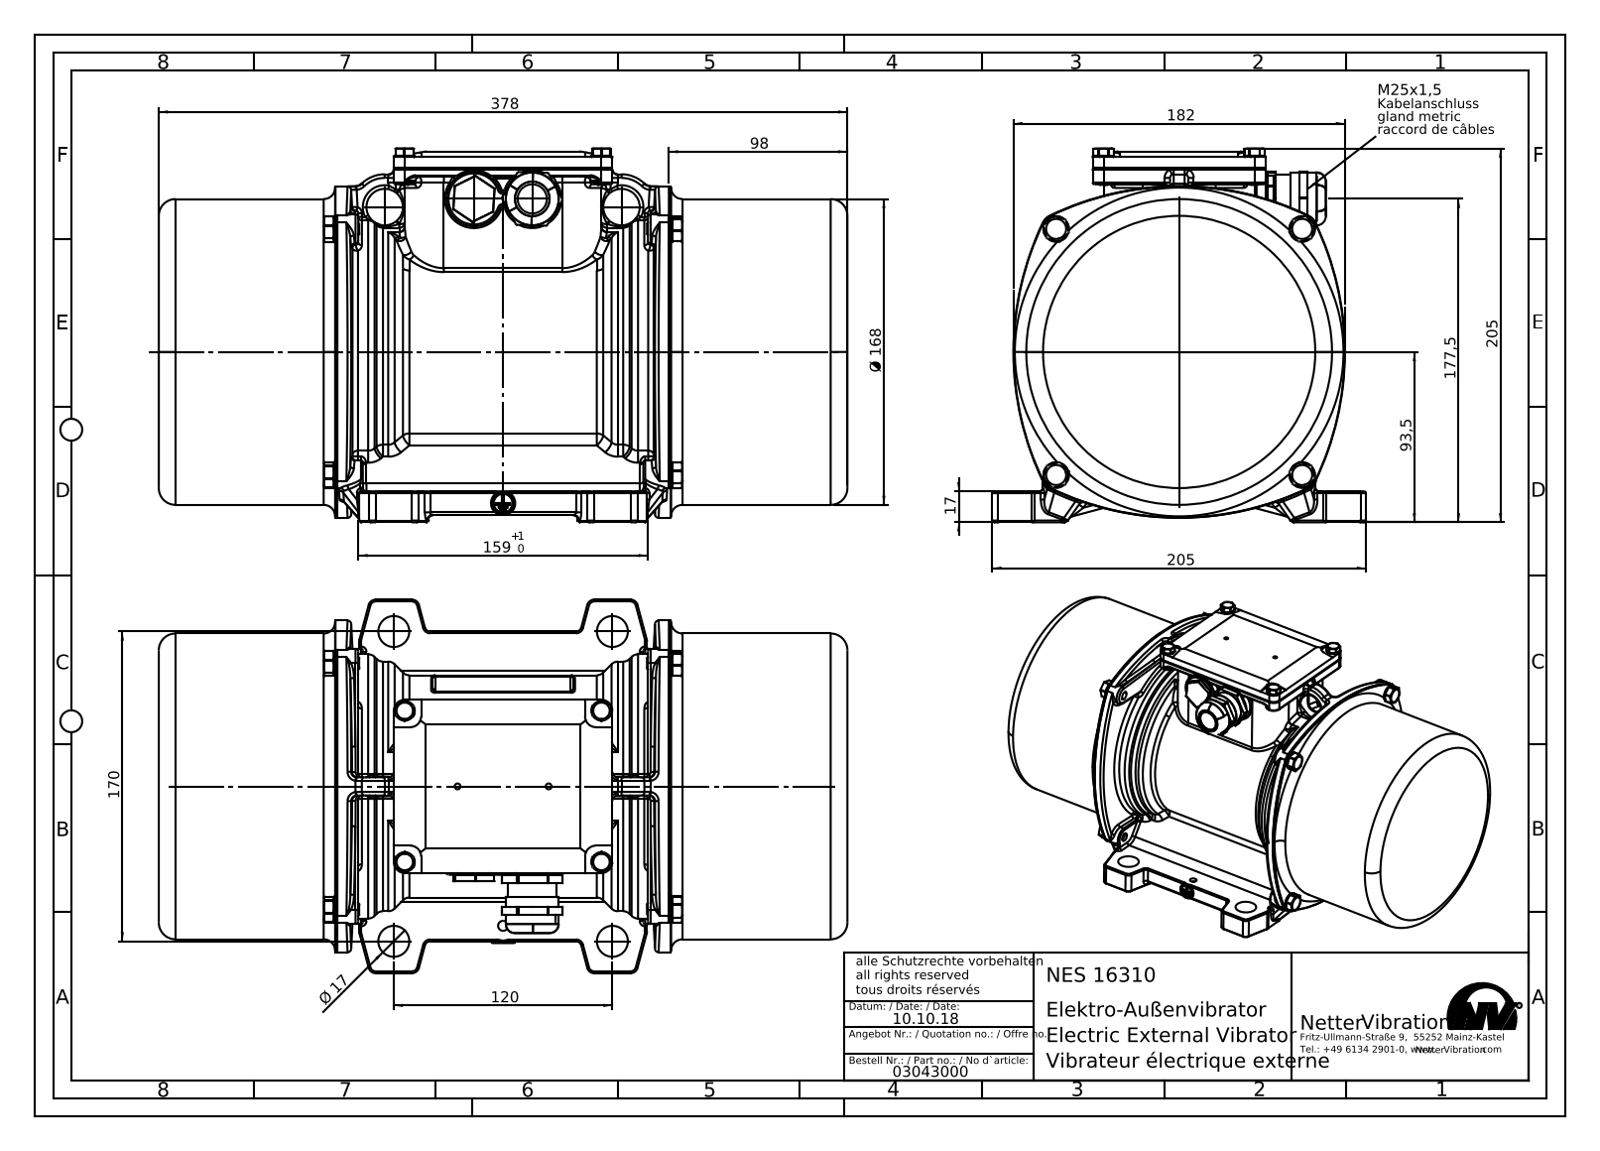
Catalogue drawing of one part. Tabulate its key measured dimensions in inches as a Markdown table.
| quantity | value |
| --- | --- |
| part name | NES 16320 #03043000 |
| STEP written by | SolidWorks 2010 (AUTOMOTIVE_DESIGN) |
| units | inches |
| bodies | 8 solids, 4055 faces (1849 planar, 731 cylindrical, 1475 other) |
| overall size | 14.882 × 8.079 × 8.071 |
| volume | 160.9 in³ |
| surface area | 1 049 in² |
| round holes (diameter × count) | 0.126 × 6, 0.197 × 4, 0.256 × 4, 0.266 × 4, 0.354 × 4, 0.669 × 4, 0.787 × 3, 0.217 × 1, 0.433 × 1, 0.63 × 1, 0.728 × 1, 0.925 × 1 |
| round bosses / shafts (diameter × count) | 0.551 × 4, 0.433 × 4, 0.315 × 4, 0.236 × 4, 0.354 × 2, 6.606 × 1, 6.496 × 1, 1.142 × 1 |
| partial cylindrical surfaces (radius × count) | 0.118 × 83, 0.02 × 78, 0.039 × 62, 0.012 × 46, 0.079 × 30, 0.059 × 16, 0.197 × 16, 0.004 × 12 |
| main face-to-face distances | 0.047, 14.835, 3.504, 11.378, 3.457, 11.331, 0.354, 11.024, 3.811, 14.787 |
| hole center spacings | 1.729, 1.993, 3.513, 3.619, 3.76, 4.733, 4.804, 4.986 |
